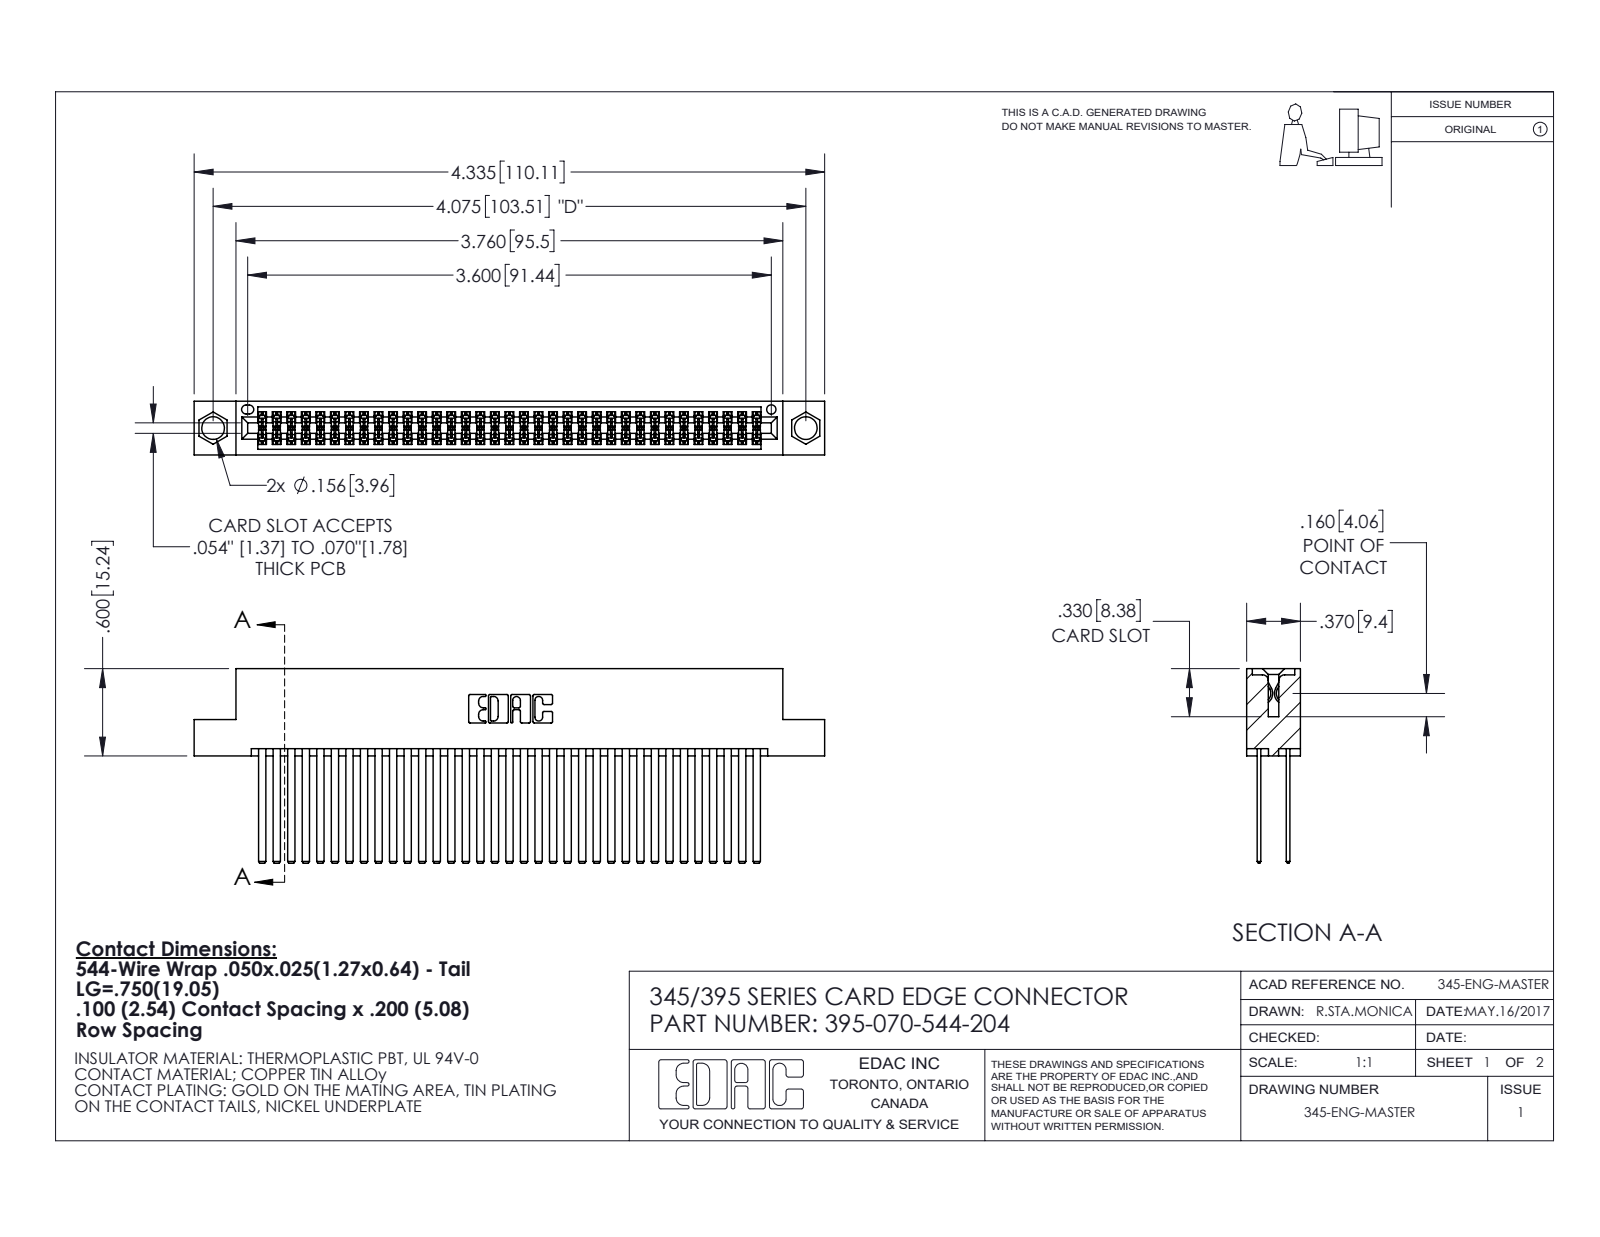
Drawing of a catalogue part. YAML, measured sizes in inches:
part_name: "345 Part_Flush Mounting Lugs - 0.156 Dia-TI; 395-070-544-204; 345-292-001_345-293-144"
step_written_by: "SolidWorks 2020 (CONFIG_CONTROL_DESIGN)"
units: inches
bodies: {solids: 71, faces: 3220, planar: 2124, cylindrical: 1096, other: 0}
overall_size: [4.335, 1.337, 0.37]
volume: 0.702
surface_area: 30.38
round_holes:
  - {diameter: 0.156, count: 2}
  - {diameter: 0.064, count: 1}
partial_cylinders:
  - {radius: 0.006, count: 140}
  - {radius: 0.01, count: 22}
  - {radius: 0.007, count: 6}
  - {radius: 0.031, count: 6}
  - {radius: 0.026, count: 3}
  - {radius: 0.014, count: 2}
  - {radius: 0.019, count: 2}
  - {radius: 0.022, count: 2}
face_to_face_distances: [0.2, 0.025, 0.072, 0.098, 0.272, 0.298, 0.225, 0.175, 0.37, 0.05]
hole_center_spacings: [0.27, 3.839, 4.075]
